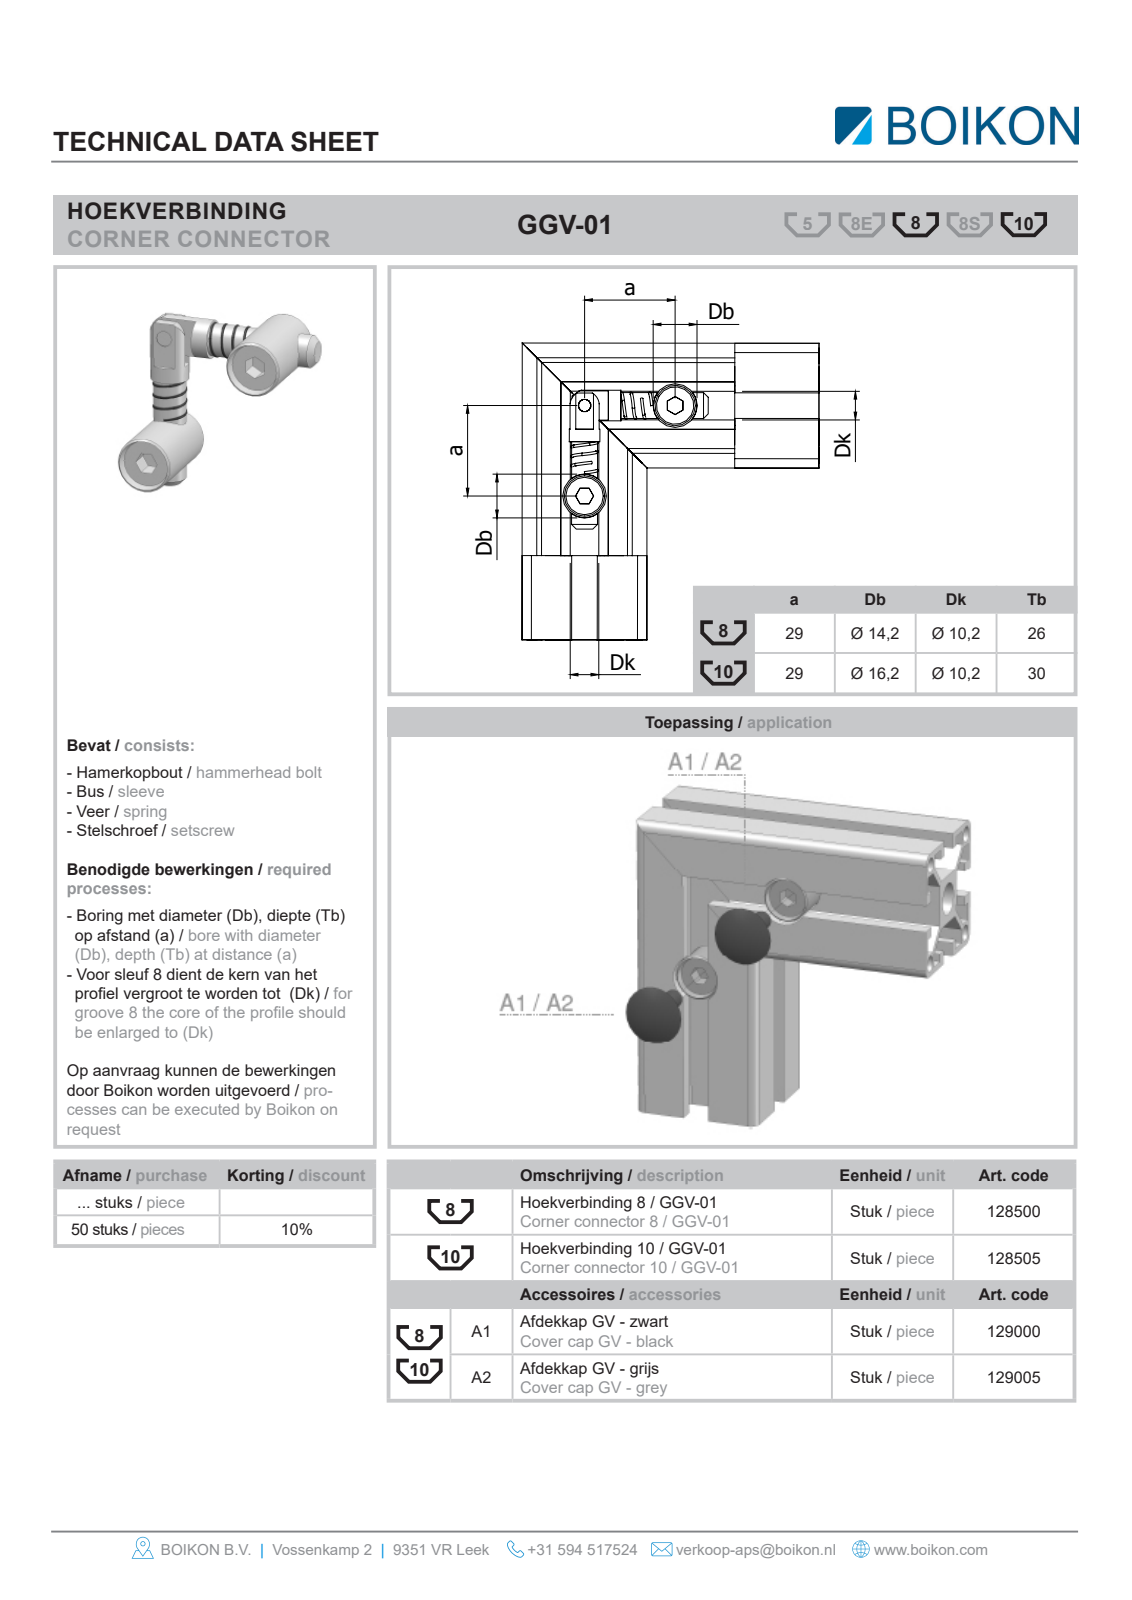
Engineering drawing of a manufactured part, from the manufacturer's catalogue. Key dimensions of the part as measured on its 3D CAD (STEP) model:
Part name (STEP PRODUCT): Root; 128505Hoekverbinding 10 / GGV-01BOIKON
STEP written by: HiCAD 2013 1802.4 Build 509 (AUTOMOTIVE_DESIGN)
Units: millimetres
Bodies: 3 solids, 58 faces (38 planar, 18 cylindrical, 2 other)
Overall size (bounding box): 47.6 × 47.6 × 29
Volume: 13 709 mm³ · Surface area: 5 984 mm²
Round holes (diameter × count): ⌀4 ×1
Round bosses / shafts (diameter × count): ⌀16 ×2, ⌀9.8 ×2, ⌀8.3 ×2
Partial cylindrical surfaces — rounded edges, fillets, slot ends (radius × count): R4.7 ×1, R5 ×1
Main face-to-face distances: 29, 6, 5.5, 2.95, 3, 2.5, 2.55, 5.45, 8, 23.45
